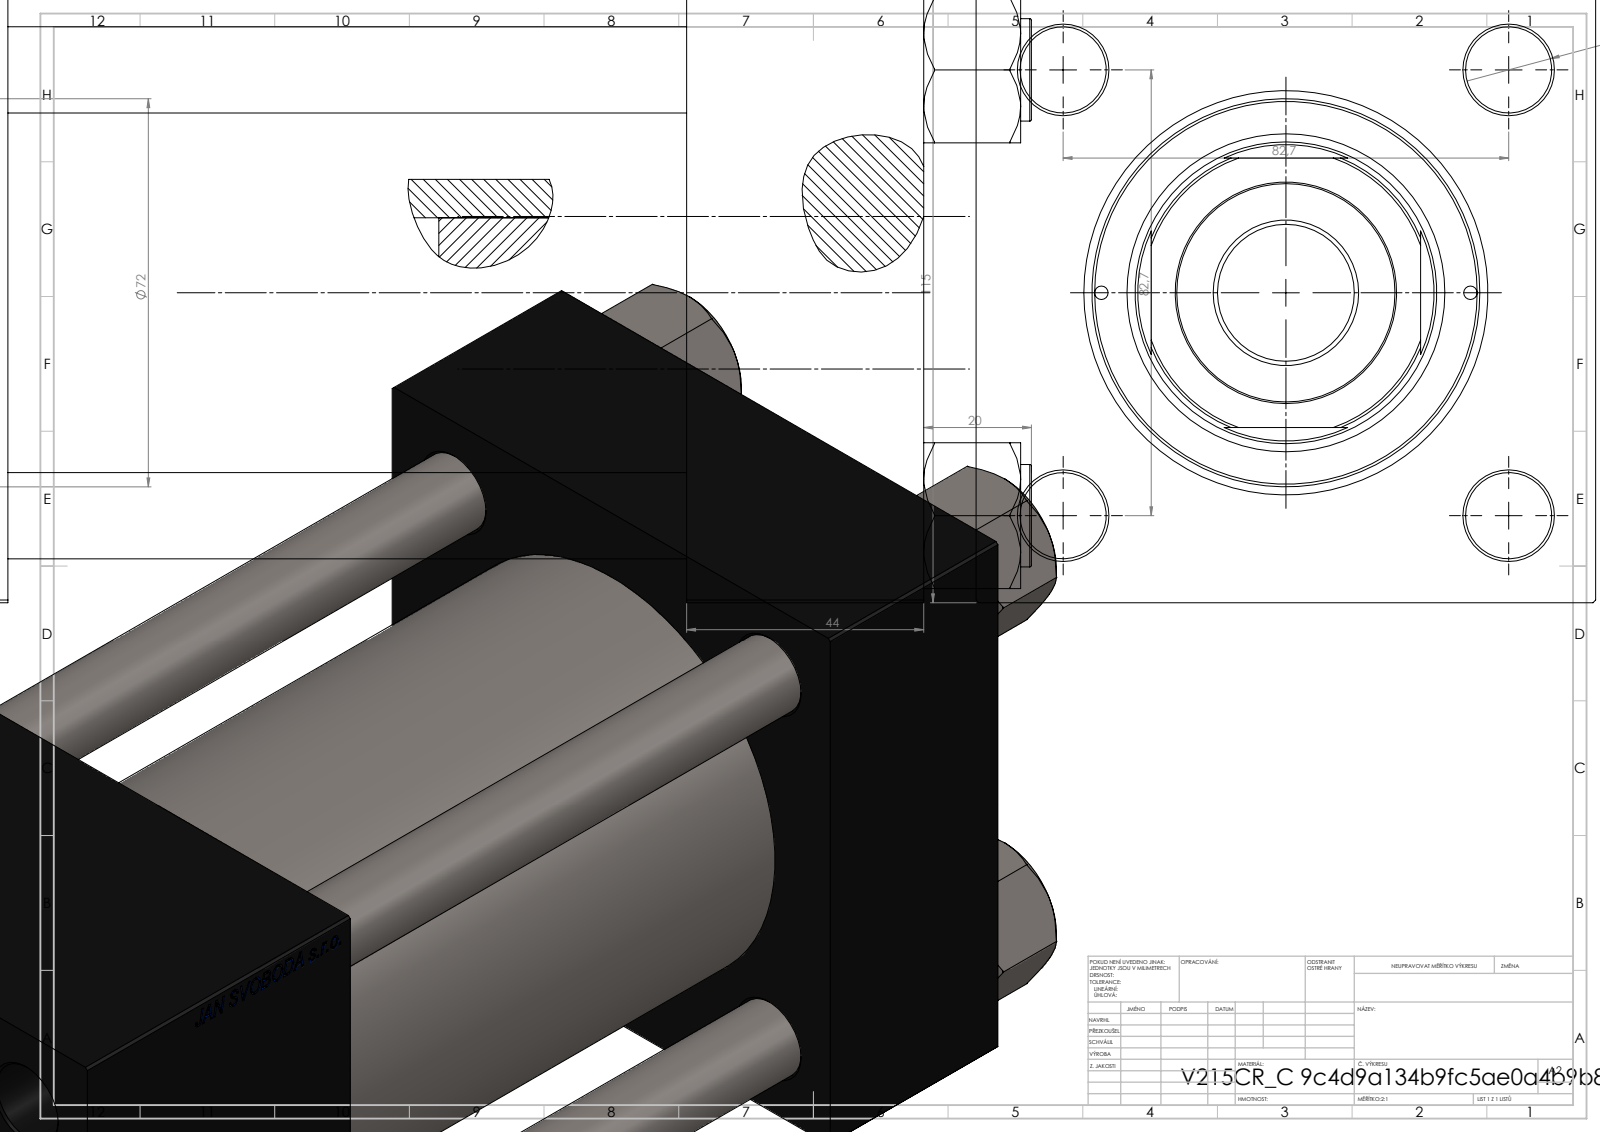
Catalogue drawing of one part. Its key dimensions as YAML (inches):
part_name: "V215_VC_A; V215CR_C_TYCINKA; V215CR_VCP_C; V215CR_C_Body (+2 more)"
step_written_by: "SolidWorks 2019 (CONFIG_CONTROL_DESIGN)"
units: inches
bodies: {solids: 12, faces: 1214, planar: 579, cylindrical: 93, other: 542}
overall_size: [12.835, 4.528, 4.528]
volume: 129.7
surface_area: 524.9
round_holes:
  - {diameter: 0.63, count: 4}
  - {diameter: 0.098, count: 2}
  - {diameter: 0.276, count: 2}
  - {diameter: 1.041, count: 2}
  - {diameter: 1.378, count: 2}
  - {diameter: 1.594, count: 1}
  - {diameter: 2.205, count: 1}
  - {diameter: 2.323, count: 1}
  - {diameter: 2.402, count: 1}
  - {diameter: 2.835, count: 1}
  - {diameter: 3.15, count: 1}
round_bosses_or_shafts:
  - {diameter: 0.748, count: 4}
  - {diameter: 3.386, count: 1}
  - {diameter: 1.063, count: 1}
  - {diameter: 0.984, count: 1}
partial_cylinders:
  - {radius: 1.063, count: 1}
face_to_face_distances: [4.528, 1.732, 6.693, 4.961, 9.409, 7.677, 2.717, 8.28, 6.547, 1.587]
hole_center_spacings: [1.652, 2.302, 3.256, 3.393, 1.348, 4.605, 2.697]
